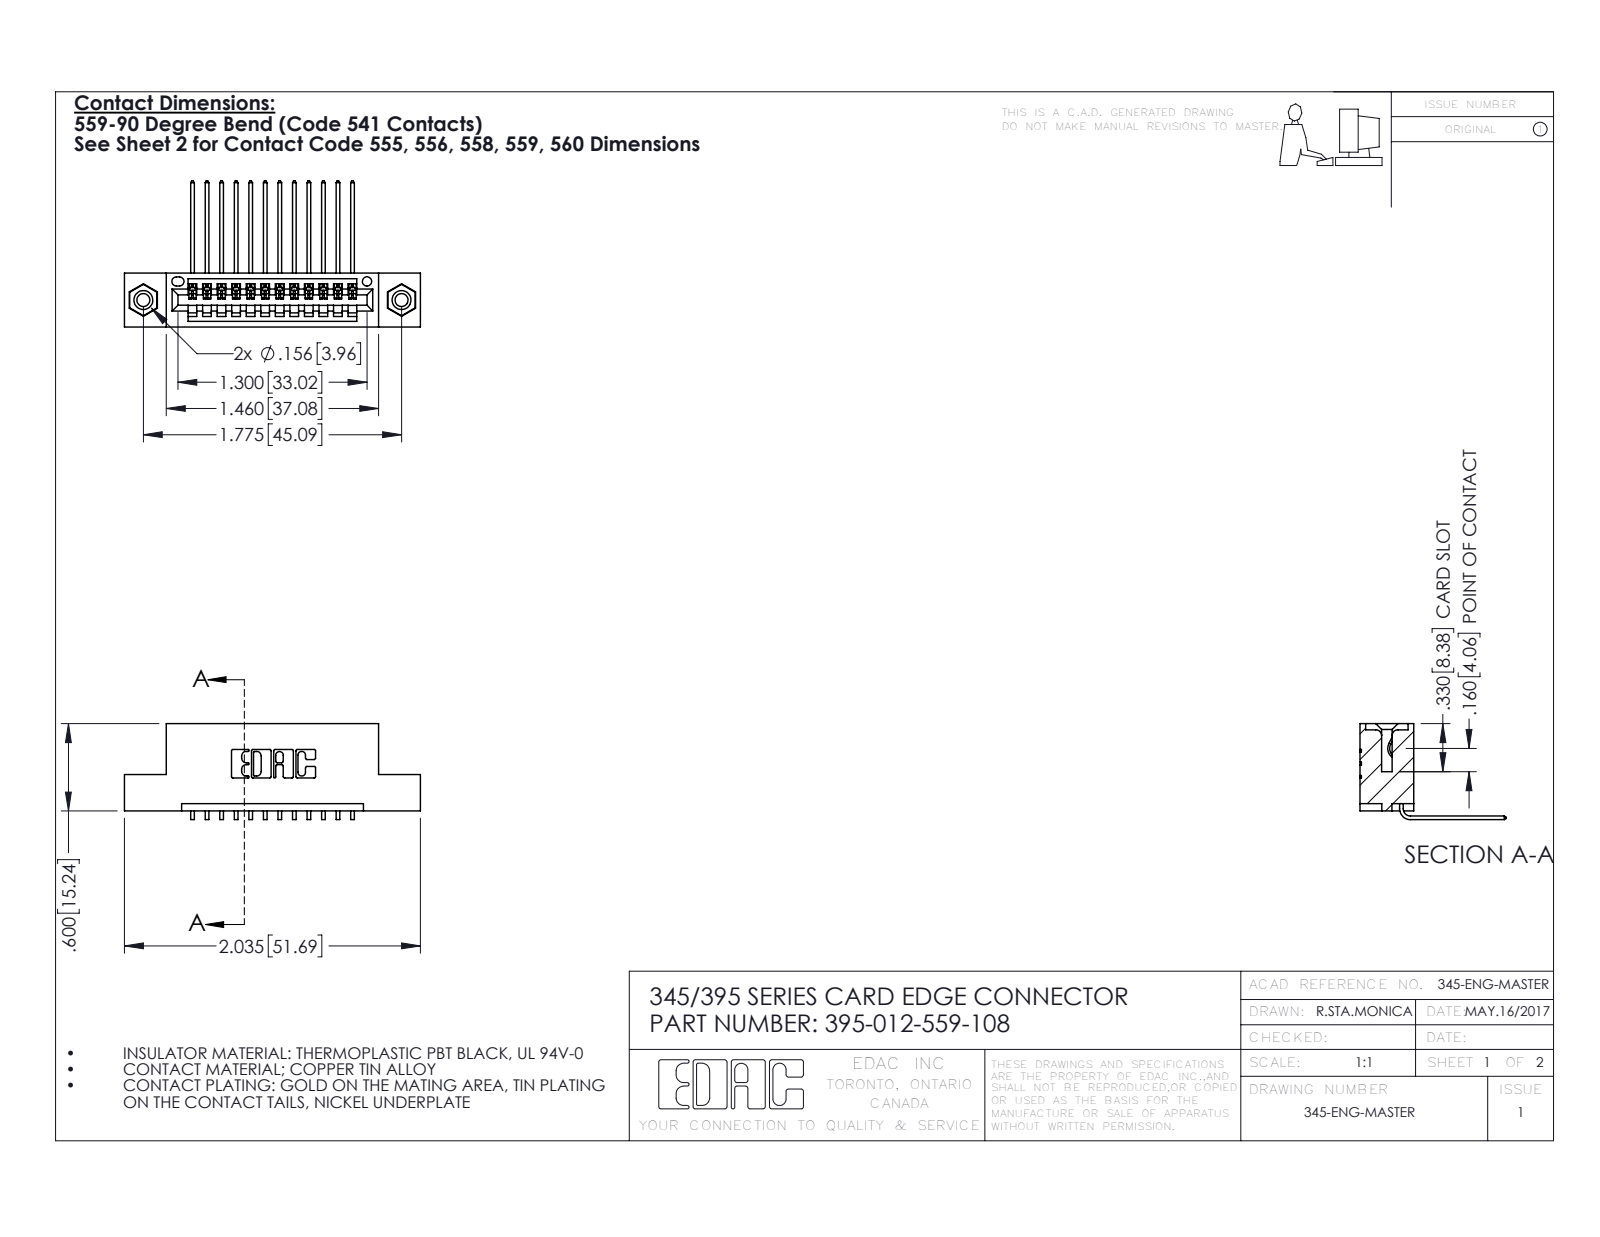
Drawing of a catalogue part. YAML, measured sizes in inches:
part_name: "345-292-001_558 559 Tail - 1; 345-250-001_345-250-003-102; 345 Part_Flush Mounting Lugs - 0.156 Dia-TI; 395-012-559-108"
step_written_by: "SolidWorks 2016 (CONFIG_CONTROL_DESIGN)"
units: inches
bodies: {solids: 15, faces: 906, planar: 616, cylindrical: 274, other: 16}
overall_size: [2.035, 1.005, 0.659]
volume: 0.287
surface_area: 9.437
round_holes:
  - {diameter: 0.089, count: 2}
  - {diameter: 0.125, count: 2}
  - {diameter: 0.156, count: 2}
  - {diameter: 0.064, count: 1}
round_bosses_or_shafts:
  - {diameter: 0.155, count: 2}
partial_cylinders:
  - {radius: 0.006, count: 24}
  - {radius: 0.01, count: 22}
  - {radius: 0.007, count: 6}
  - {radius: 0.031, count: 6}
  - {radius: 0.026, count: 3}
  - {radius: 0.031, count: 2}
  - {radius: 0.04, count: 2}
  - {radius: 0.014, count: 1}
face_to_face_distances: [0.2, 0.072, 0.298, 0.37, 0.098, 0.272, 0.025, 0.1, 0.6, 0.3]
hole_center_spacings: [0.27, 1.543, 1.775]
